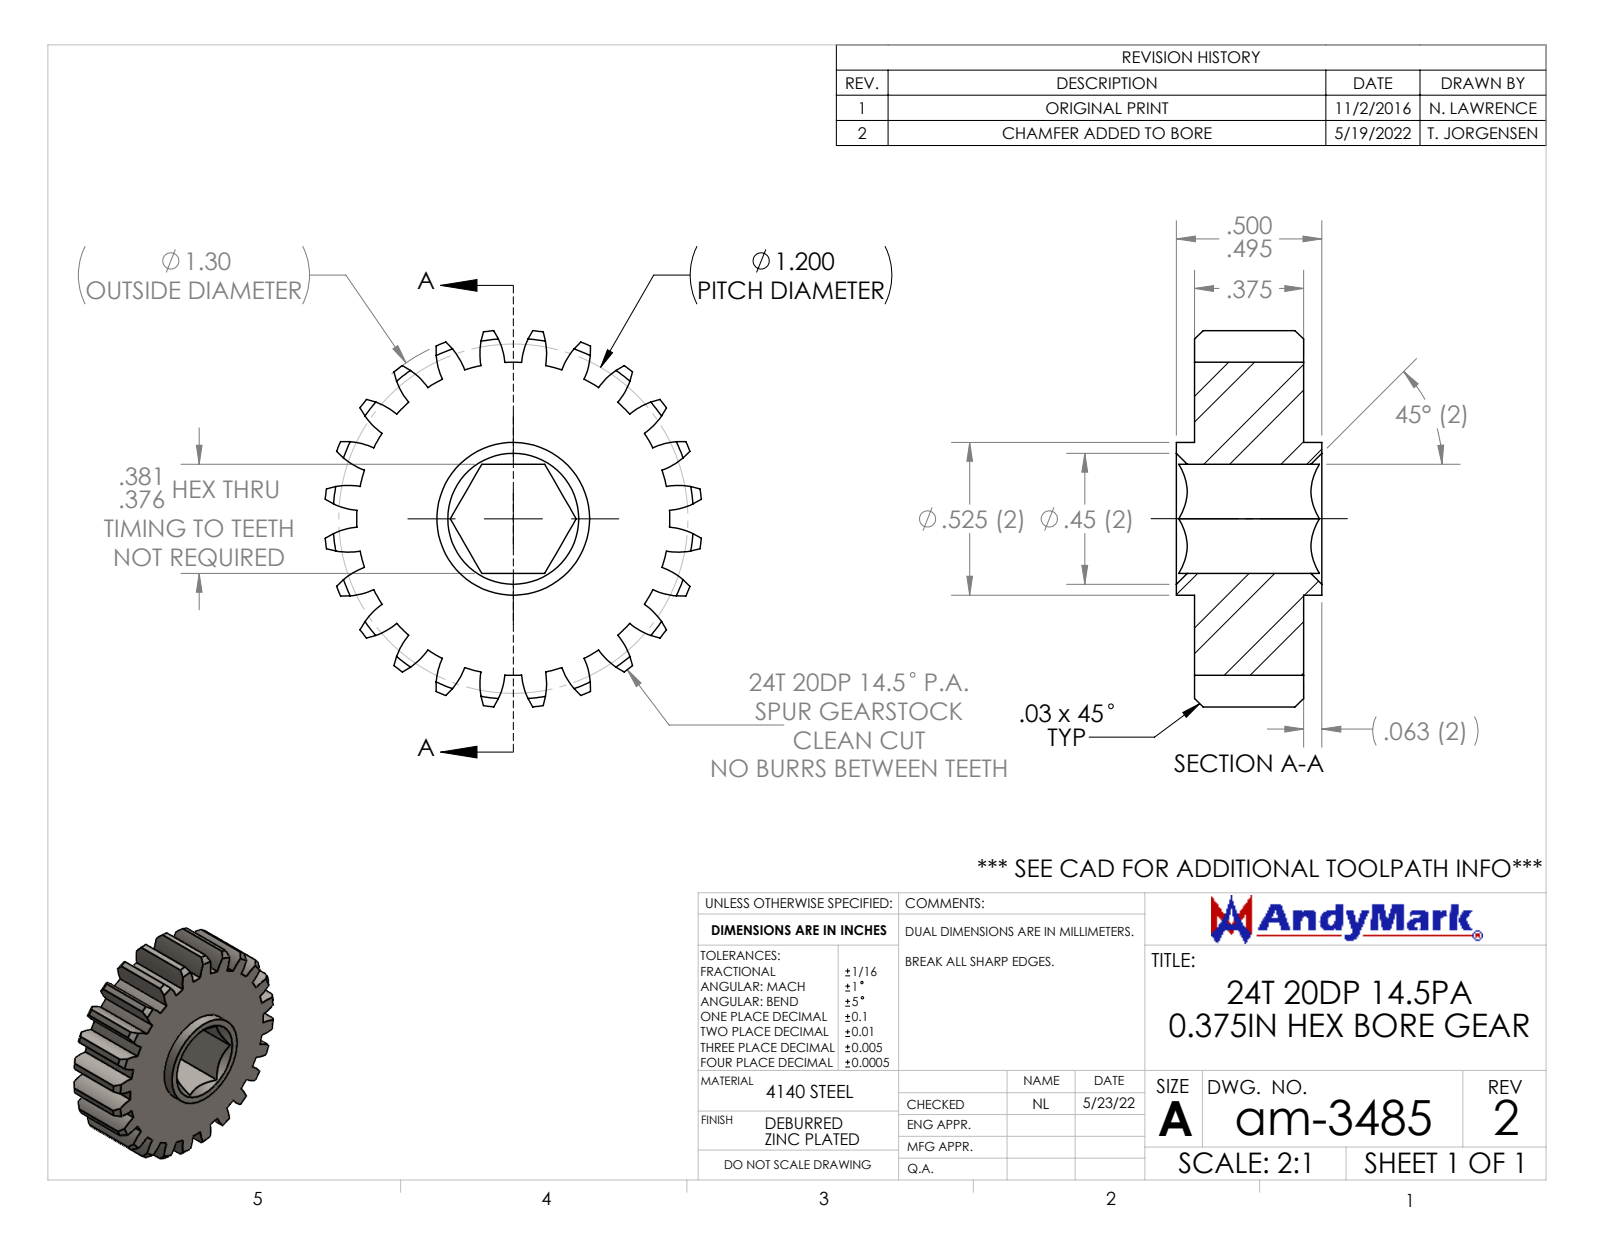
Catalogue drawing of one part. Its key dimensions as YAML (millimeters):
part_name: "am-3485 24T 20DP 375hex 375 FW"
step_written_by: "SolidWorks 2021 (CONFIG_CONTROL_DESIGN)"
units: millimeters
bodies: {solids: 1, faces: 167, planar: 10, cylindrical: 105, other: 52}
overall_size: [32.8, 32.8, 12.7]
volume: 6150
surface_area: 3640
round_bosses_or_shafts:
  - {diameter: 13.3, count: 1}
partial_cylinders:
  - {radius: 6.1, count: 48}
  - {radius: 13.7, count: 1}
  - {radius: 16.5, count: 1}
face_to_face_distances: [9.5, 9.5, 1.6, 11.1, 12.7, 11.1, 1.6]
